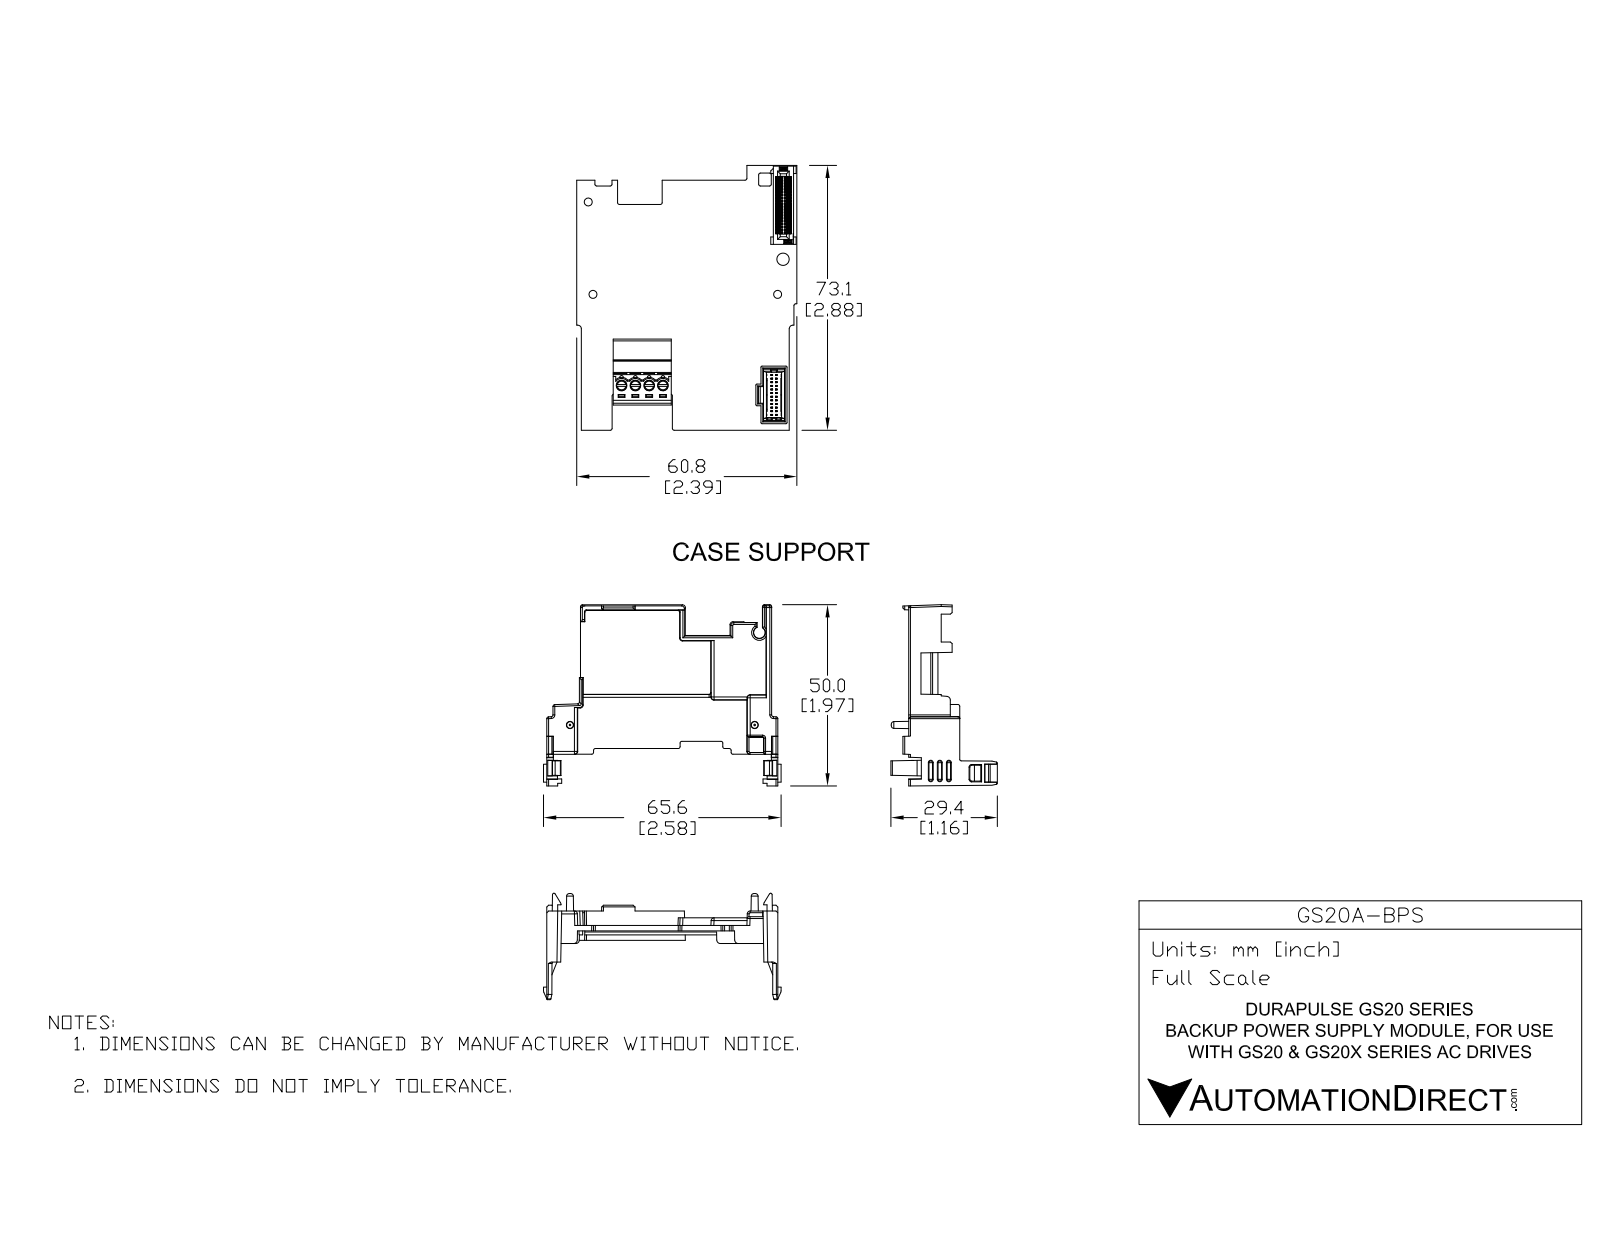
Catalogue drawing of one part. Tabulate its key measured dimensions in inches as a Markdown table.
| quantity | value |
| --- | --- |
| part name | GS20A-BPS |
| STEP written by | SolidWorks 2017 (AUTOMOTIVE_DESIGN) |
| units | inches |
| bodies | 5 solids, 6573 faces (4869 planar, 1419 cylindrical, 285 other) |
| overall size | 2.878 × 2.583 × 1.335 |
| volume | 1.015 in³ |
| surface area | 40.45 in² |
| round holes (diameter × count) | 0.045 × 2, 0.087 × 2, 0.134 × 1 |
| round bosses / shafts (diameter × count) | 0.073 × 4, 0.05 × 2, 0.236 × 1, 0.213 × 1, 0.118 × 1, 0.087 × 1, 0.033 × 1, 0.022 × 1 |
| partial cylindrical surfaces (radius × count) | 0.006 × 412, 0.02 × 88, 0.004 × 60, 0.008 × 46, 0.039 × 31, 0.012 × 30, 0.01 × 16, 0.031 × 16 |
| main face-to-face distances | 0.063, 0.059, 0.043, 0.264, 0.22, 0.201, 0.157, 0.016, 0.126, 0.323 |
| hole center spacings | 0.387, 0.45, 0.793, 1.053, 1.447, 1.717, 1.849, 2.007 |
